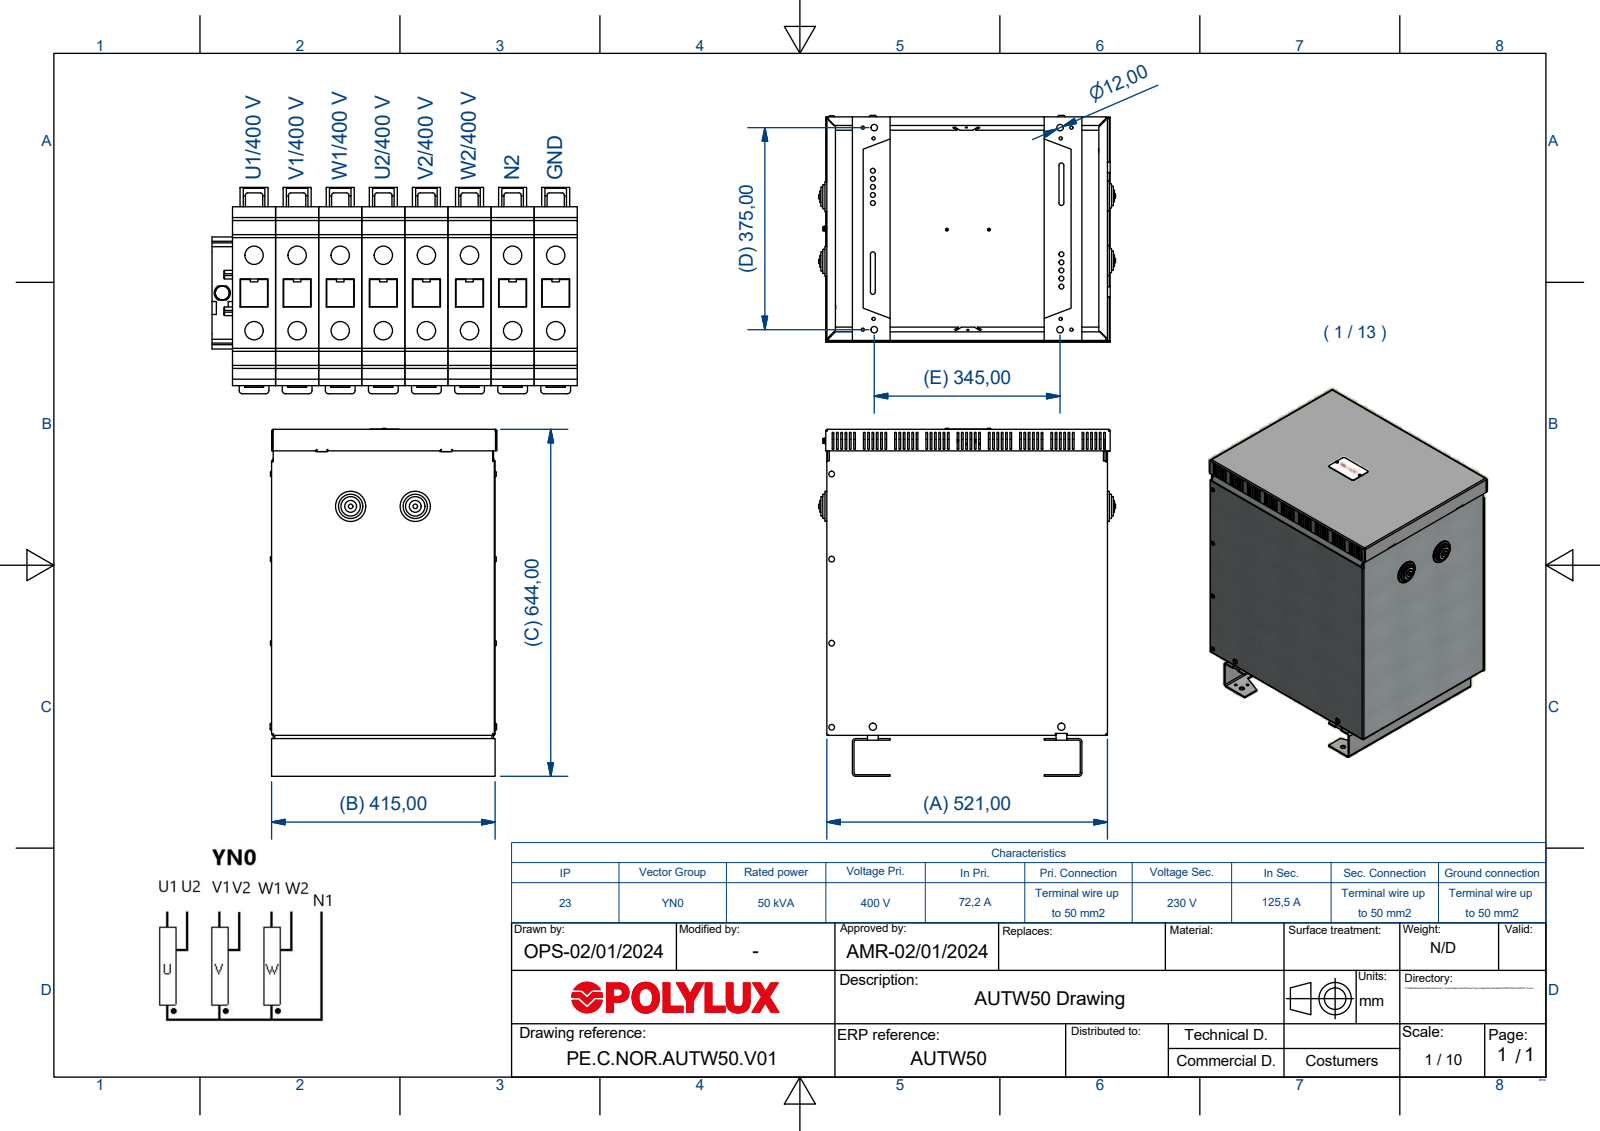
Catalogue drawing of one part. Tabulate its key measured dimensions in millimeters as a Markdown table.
| quantity | value |
| --- | --- |
| part name | AUTX50 |
| STEP written by | Autodesk Inventor 2018 (AUTOMOTIVE_DESIGN) |
| units | millimeters |
| bodies | 45 solids, 3789 faces (2909 planar, 790 cylindrical, 90 other) |
| overall size | 442.9 × 420 × 215 |
| volume | 25 470 000 mm³ |
| surface area | 2 575 000 mm² |
| round holes (diameter × count) | 9 × 18, 8.5 × 16, 6.65 × 12, 12 × 10, 3.5 × 6, 4.5 × 2, 2 × 1 |
| round bosses / shafts (diameter × count) | 16 × 6, 8 × 6, 4 × 2 |
| partial cylindrical surfaces (radius × count) | 1 × 51, 4.5 × 24, 10 × 24, 0.5 × 22, 1.5 × 16, 2 × 15, 4 × 12, 5.5 × 6 |
| main face-to-face distances | 140, 3, 2, 32, 108, 280, 123, 1, 74, 105 |
| hole center spacings | 70, 123, 288.62, 35, 280, 350, 22.09, 37.55 |
